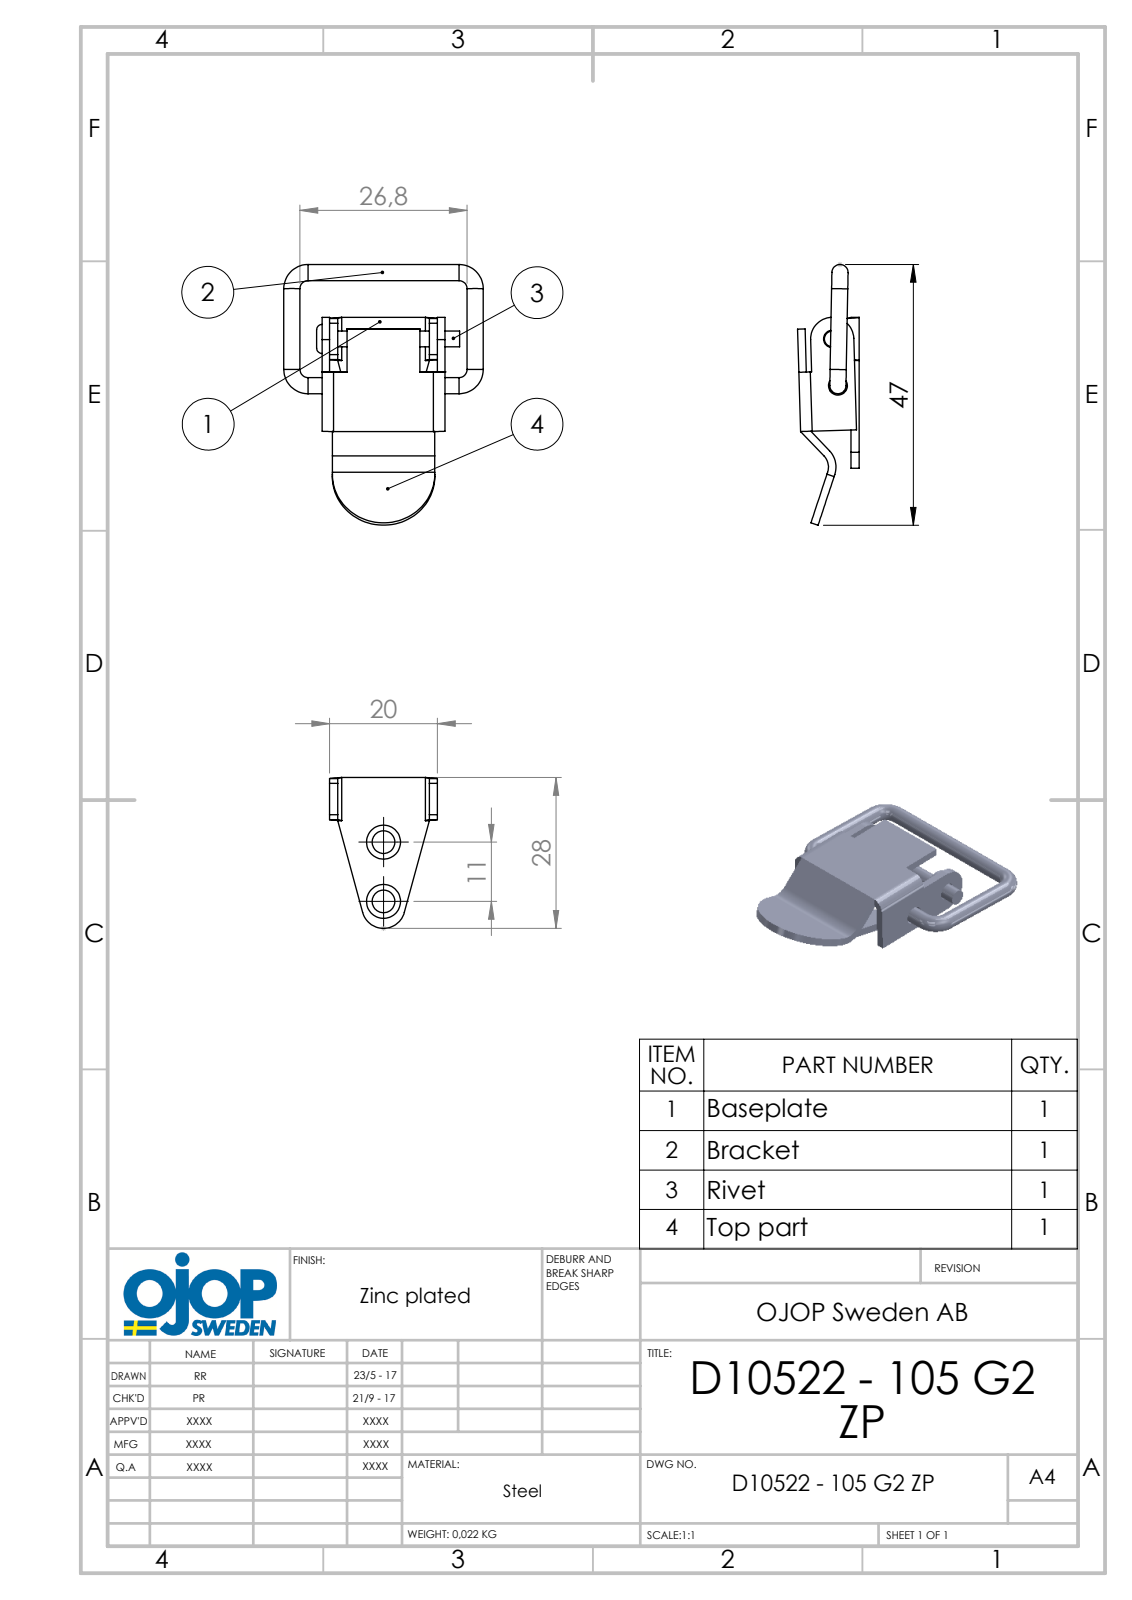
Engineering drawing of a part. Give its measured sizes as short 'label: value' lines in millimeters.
name: överdel; nit; 10522 - 105 G2 ZP; bygel (+1 more)
written by: SolidWorks 2015 (AUTOMOTIVE_DESIGN)
unit: mm
bodies: 4 solids, 129 faces (67 planar, 48 cylindrical, 14 other)
size: 62.97 × 36.91 × 11.43
volume: 3 054 mm³; area: 4 814 mm²
holes: 2× ⌀4.2, 1× ⌀3.2, 1× ⌀3.5
bosses: 4× ⌀3, 1× ⌀2.9
rounds: 4× R0.74, 2× R2.14, 2× R2.24, 2× R3, 2× R4, 1× R4.4, 1× R9.5
face distances: 1.4, 1.5, 21.4, 20, 22.8, 1.9, 2.9, 19.9, 18.5, 8.98
hole spacings: 8.74, 11
